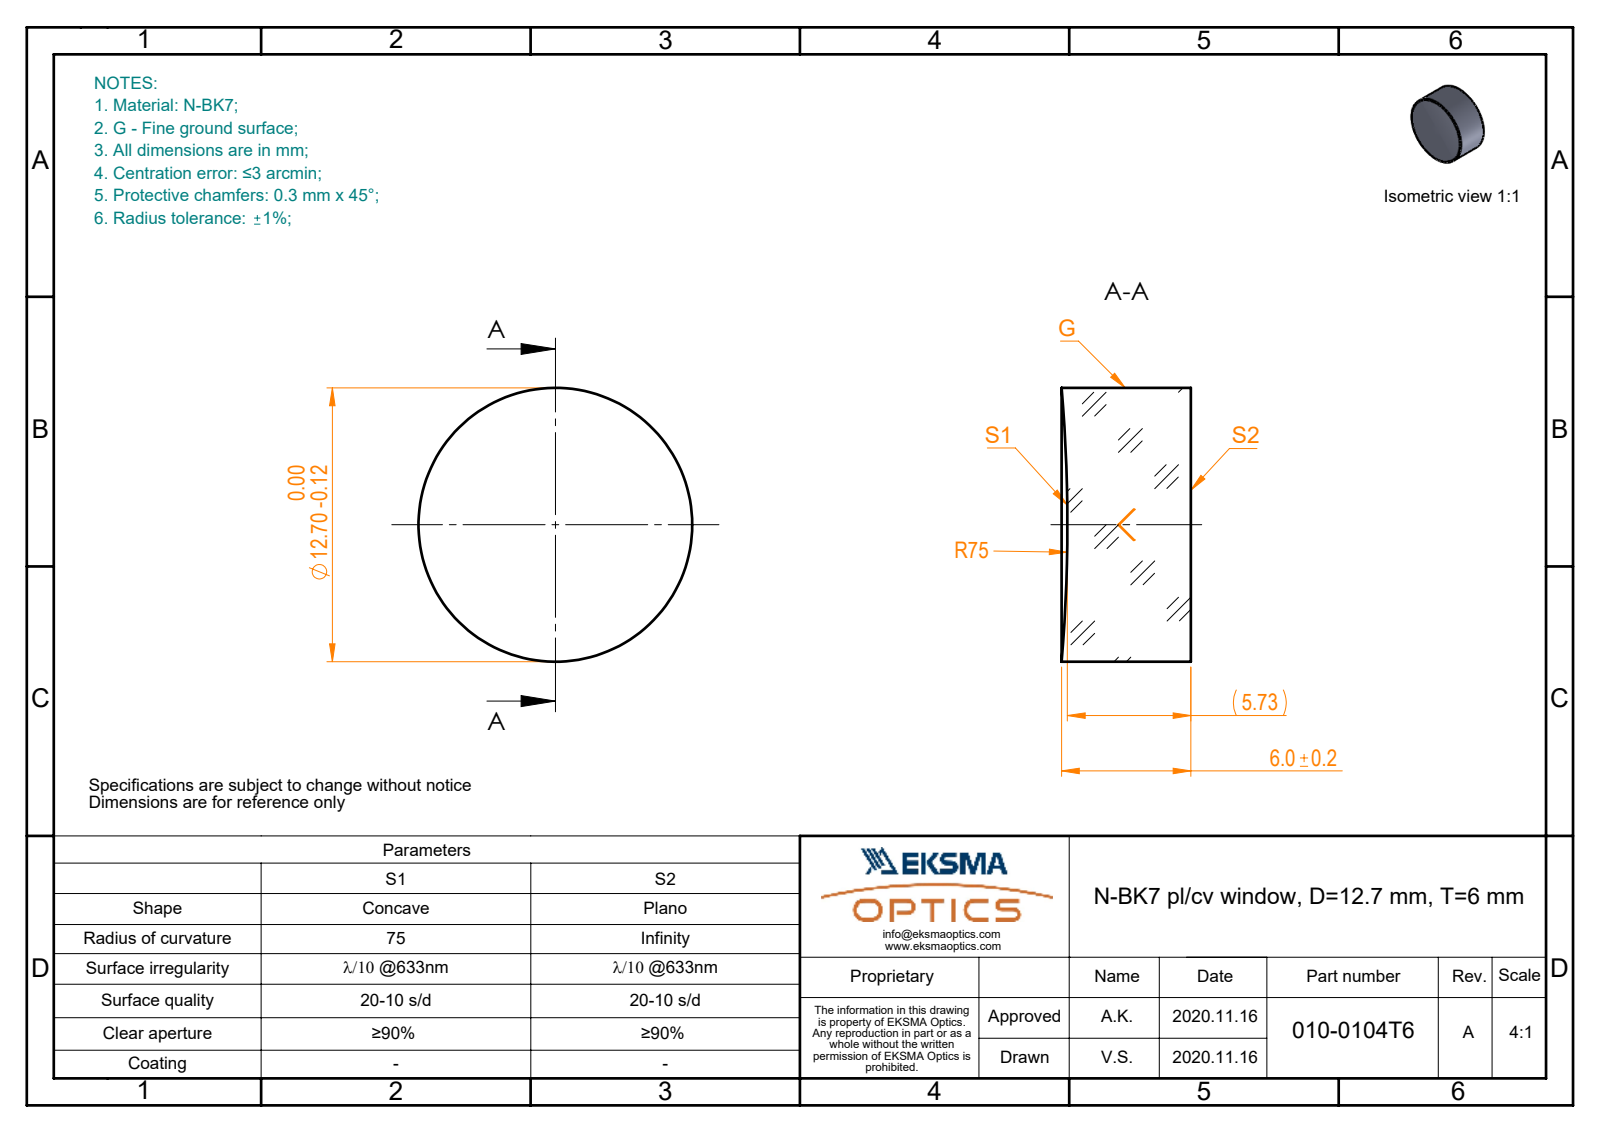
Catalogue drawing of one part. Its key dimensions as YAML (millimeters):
part_name: "010-0104T6_N-BK7_PCV_window"
step_written_by: "SolidWorks 2019 (CONFIG_CONTROL_DESIGN)"
units: millimeters
bodies: {solids: 1, faces: 5, planar: 1, cylindrical: 2, other: 2}
overall_size: [12.7, 12.7, 6]
volume: 743
surface_area: 493
round_bosses_or_shafts:
  - {diameter: 12.7, count: 1}
